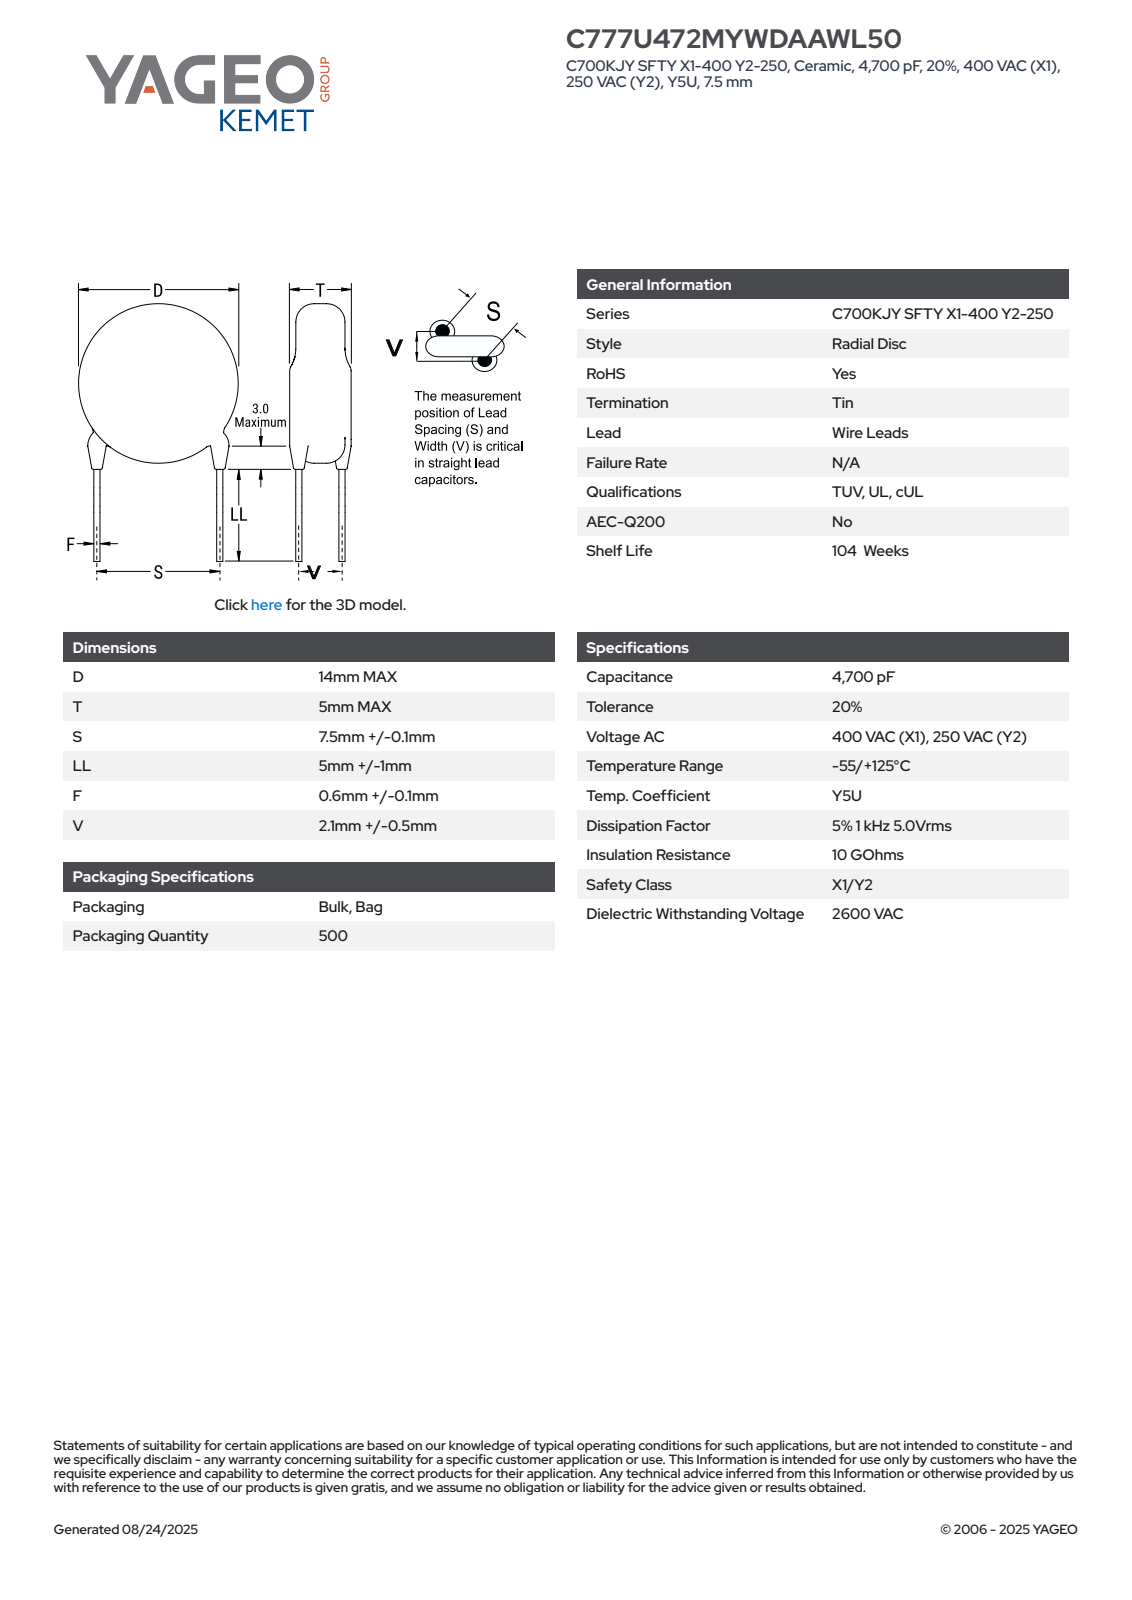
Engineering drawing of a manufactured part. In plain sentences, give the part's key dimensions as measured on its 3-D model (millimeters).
The part is named "CCD_KST_14X5_D14T5S7.6LL6F0.7V2.1". Its 3-D file was written by "SolidWorks 2021 (AUTOMOTIVE_DESIGN)". It is 4 solids with 77 faces: 63 planar, 10 cylindrical and 4 other. Overall it measures 20.38 by 14 by 5 millimeters. Its volume is 759 cubic millimeters and its surface area 543 square millimeters. Round bosses or shafts: 2 of diameter 1.2, 2 of diameter 0.7, 1 of diameter 14. The main face-to-face distances are 5, 6, 14.58, 8.58, 12.93, 6.93, 1.65, 0.45, 6.74, 0.32.
